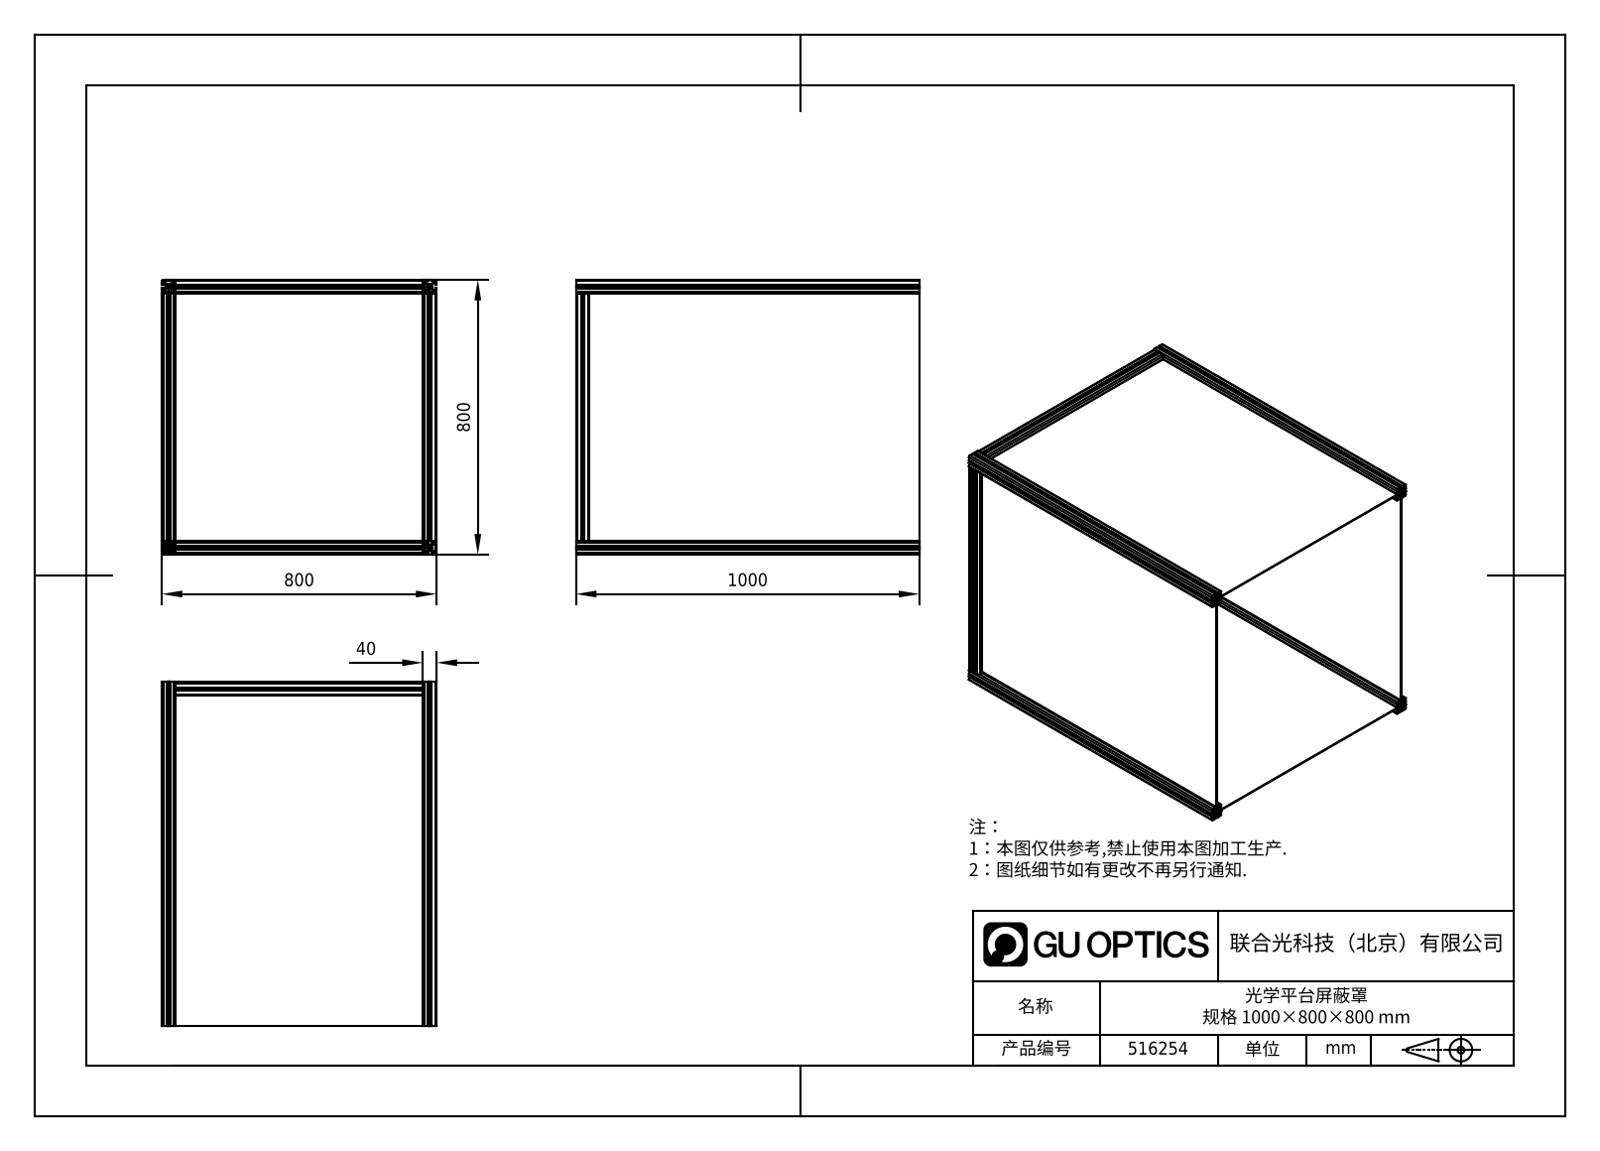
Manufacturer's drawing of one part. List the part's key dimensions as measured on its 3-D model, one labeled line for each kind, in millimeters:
Part name (STEP PRODUCT): 516254; 光学平台屏蔽罩边框_720; 光学平台屏蔽罩面板_744_972; 光学平台屏蔽罩边框_1000 (+2 more)
STEP written by: SolidWorks 2020 (CONFIG_CONTROL_DESIGN)
Units: millimetres
Bodies: 13 solids, 1230 faces (950 planar, 280 cylindrical, 0 other)
Overall size (bounding box): 1000 × 800 × 800
Volume: 10 970 000 mm³ · Surface area: 10 270 000 mm²
Partial cylindrical surfaces — rounded edges, fillets, slot ends (radius × count): R0.5 ×64, R1 ×64, R0.75 ×32, R2.5 ×32, R4.5 ×32, R3.4 ×8
Main face-to-face distances: 2, 760, 762, 758, 19, 21, 8.2, 31.8, 10.8, 12.8
